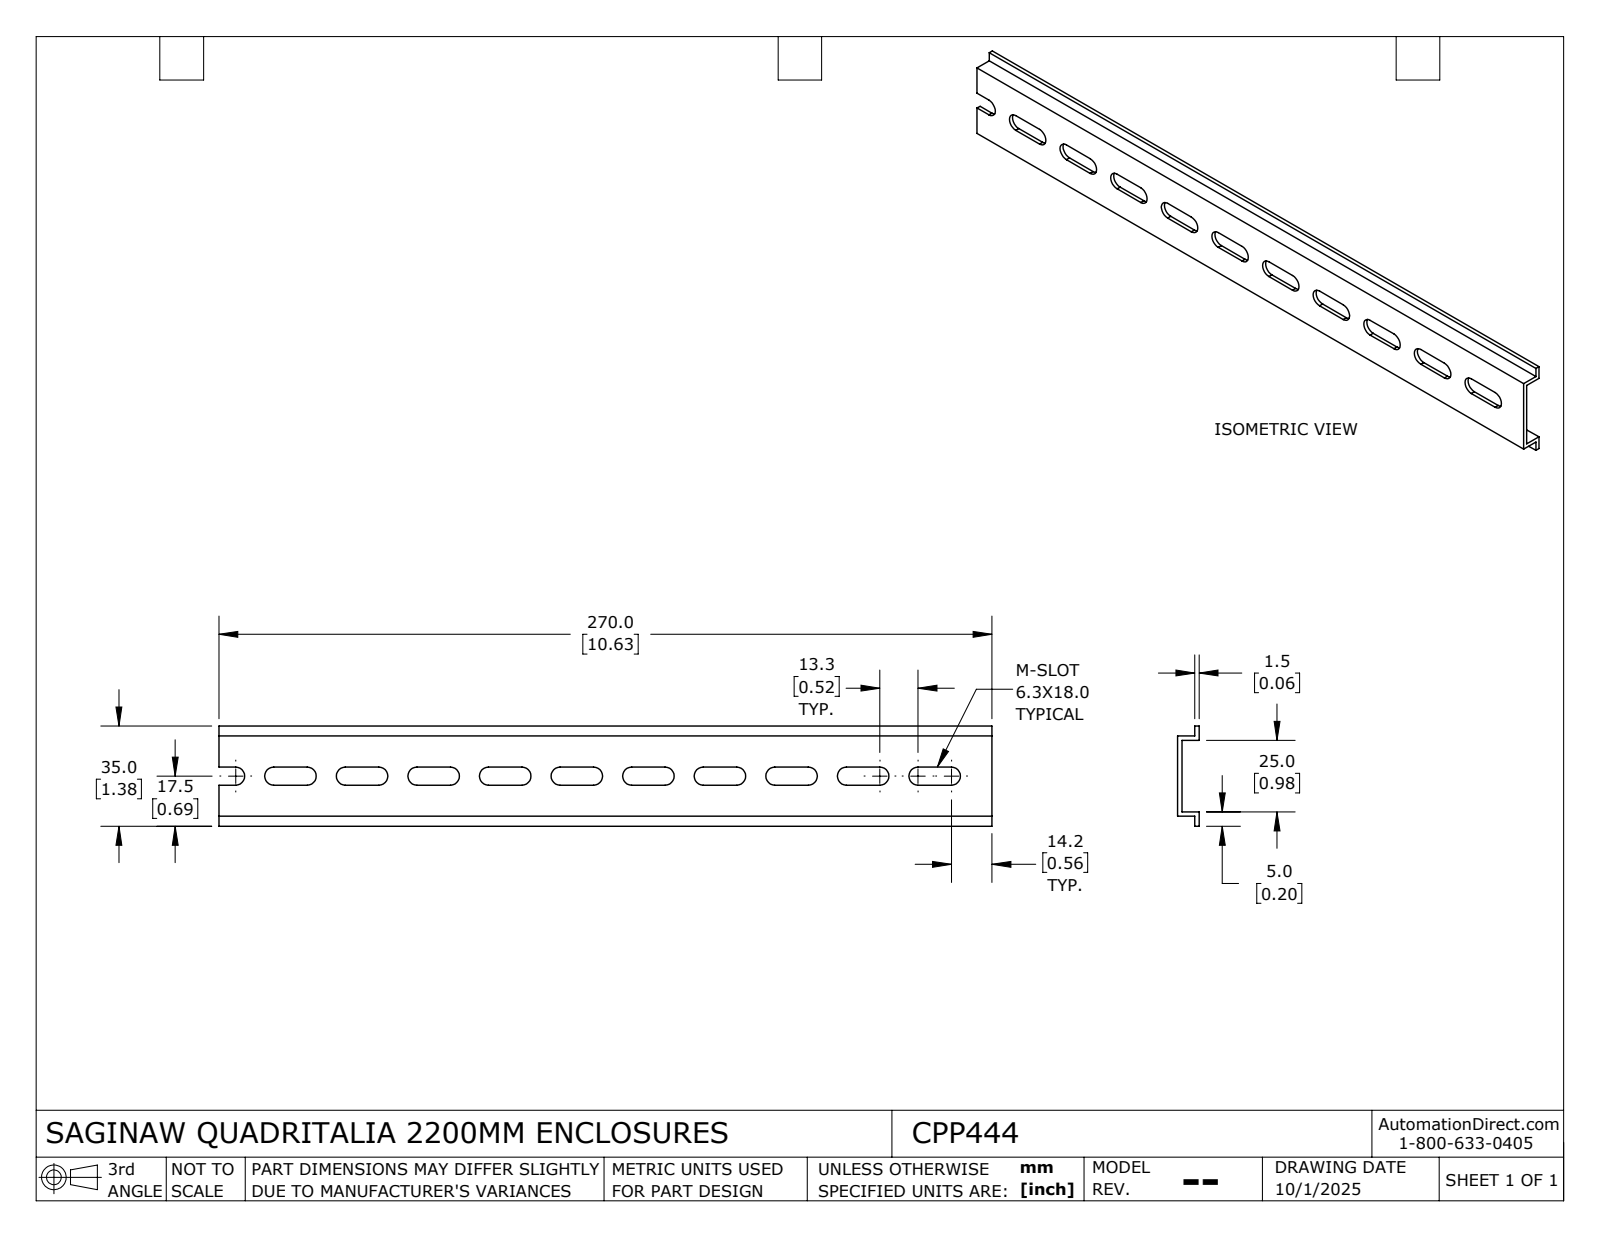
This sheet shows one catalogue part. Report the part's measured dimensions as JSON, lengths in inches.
{"part_name": "CPP444_Default", "step_written_by": "SolidWorks 2024 (CONFIG_CONTROL_DESIGN)", "units": "inches", "bodies": {"solids": 1, "faces": 58, "planar": 37, "cylindrical": 21, "other": 0}, "overall_size": [10.63, 1.378, 0.295], "volume_in3": 1.061, "surface_area_in2": 38.44, "partial_cylinders_radius": [[0.124, 21]], "face_to_face_distances": [0.059, 0.236, 1.043, 0.295, 0.177, 1.102, 0.984, 0.138, 0.197, 1.181]}
